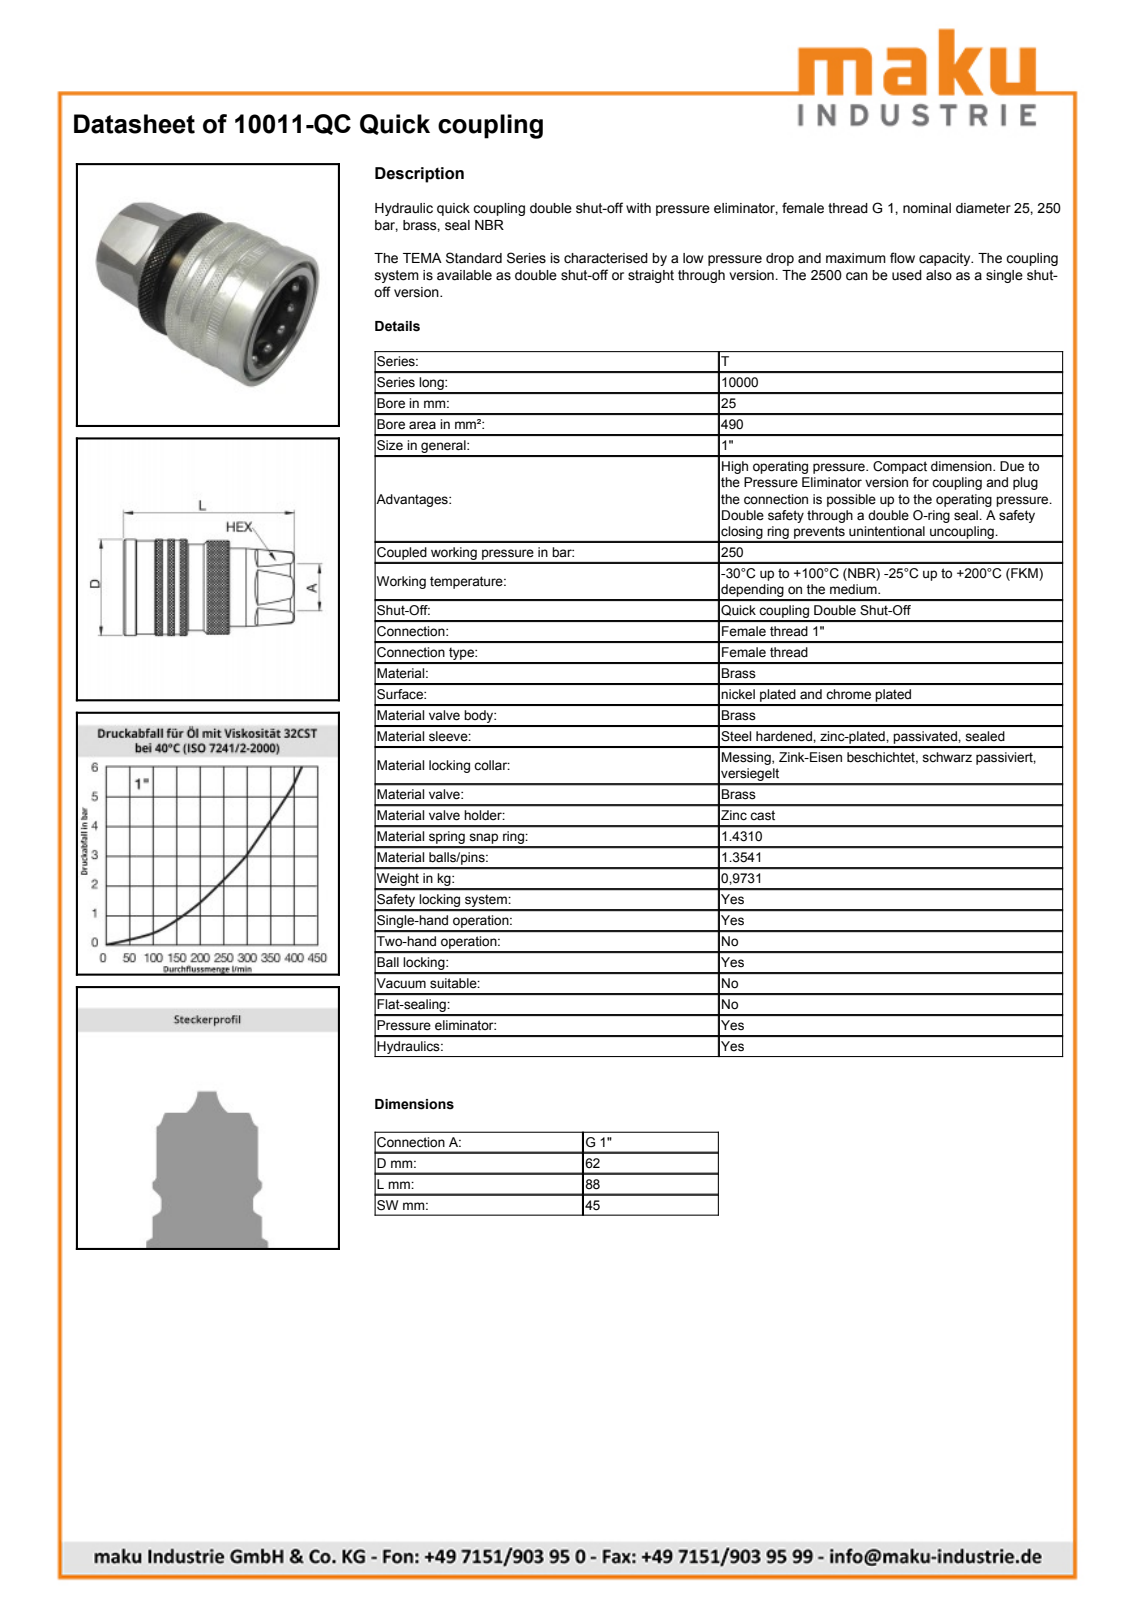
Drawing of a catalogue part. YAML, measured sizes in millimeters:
part_name: "10011-QC"
step_written_by: "SolidWorks 2009 (AUTOMOTIVE_DESIGN)"
units: millimeters
bodies: {solids: 1, faces: 148, planar: 36, cylindrical: 44, other: 68}
overall_size: [88.3, 62, 62]
volume: 149828
surface_area: 32608
round_holes:
  - {diameter: 3.93, count: 1}
  - {diameter: 24.4, count: 1}
  - {diameter: 30.6, count: 1}
  - {diameter: 41, count: 1}
  - {diameter: 41, count: 1}
  - {diameter: 43.4, count: 1}
  - {diameter: 44.1, count: 1}
  - {diameter: 47.3, count: 1}
  - {diameter: 53, count: 1}
  - {diameter: 55.2, count: 1}
  - {diameter: 56.4, count: 1}
round_bosses_or_shafts:
  - {diameter: 62, count: 1}
  - {diameter: 61, count: 1}
  - {diameter: 60.7, count: 1}
  - {diameter: 59, count: 1}
  - {diameter: 54.5, count: 1}
  - {diameter: 51.6, count: 1}
  - {diameter: 49.6, count: 1}
face_to_face_distances: [45, 35.6, 31.2, 66.8, 21.5, 52.7, 88.3, 3.9, 48.8, 27.3]
